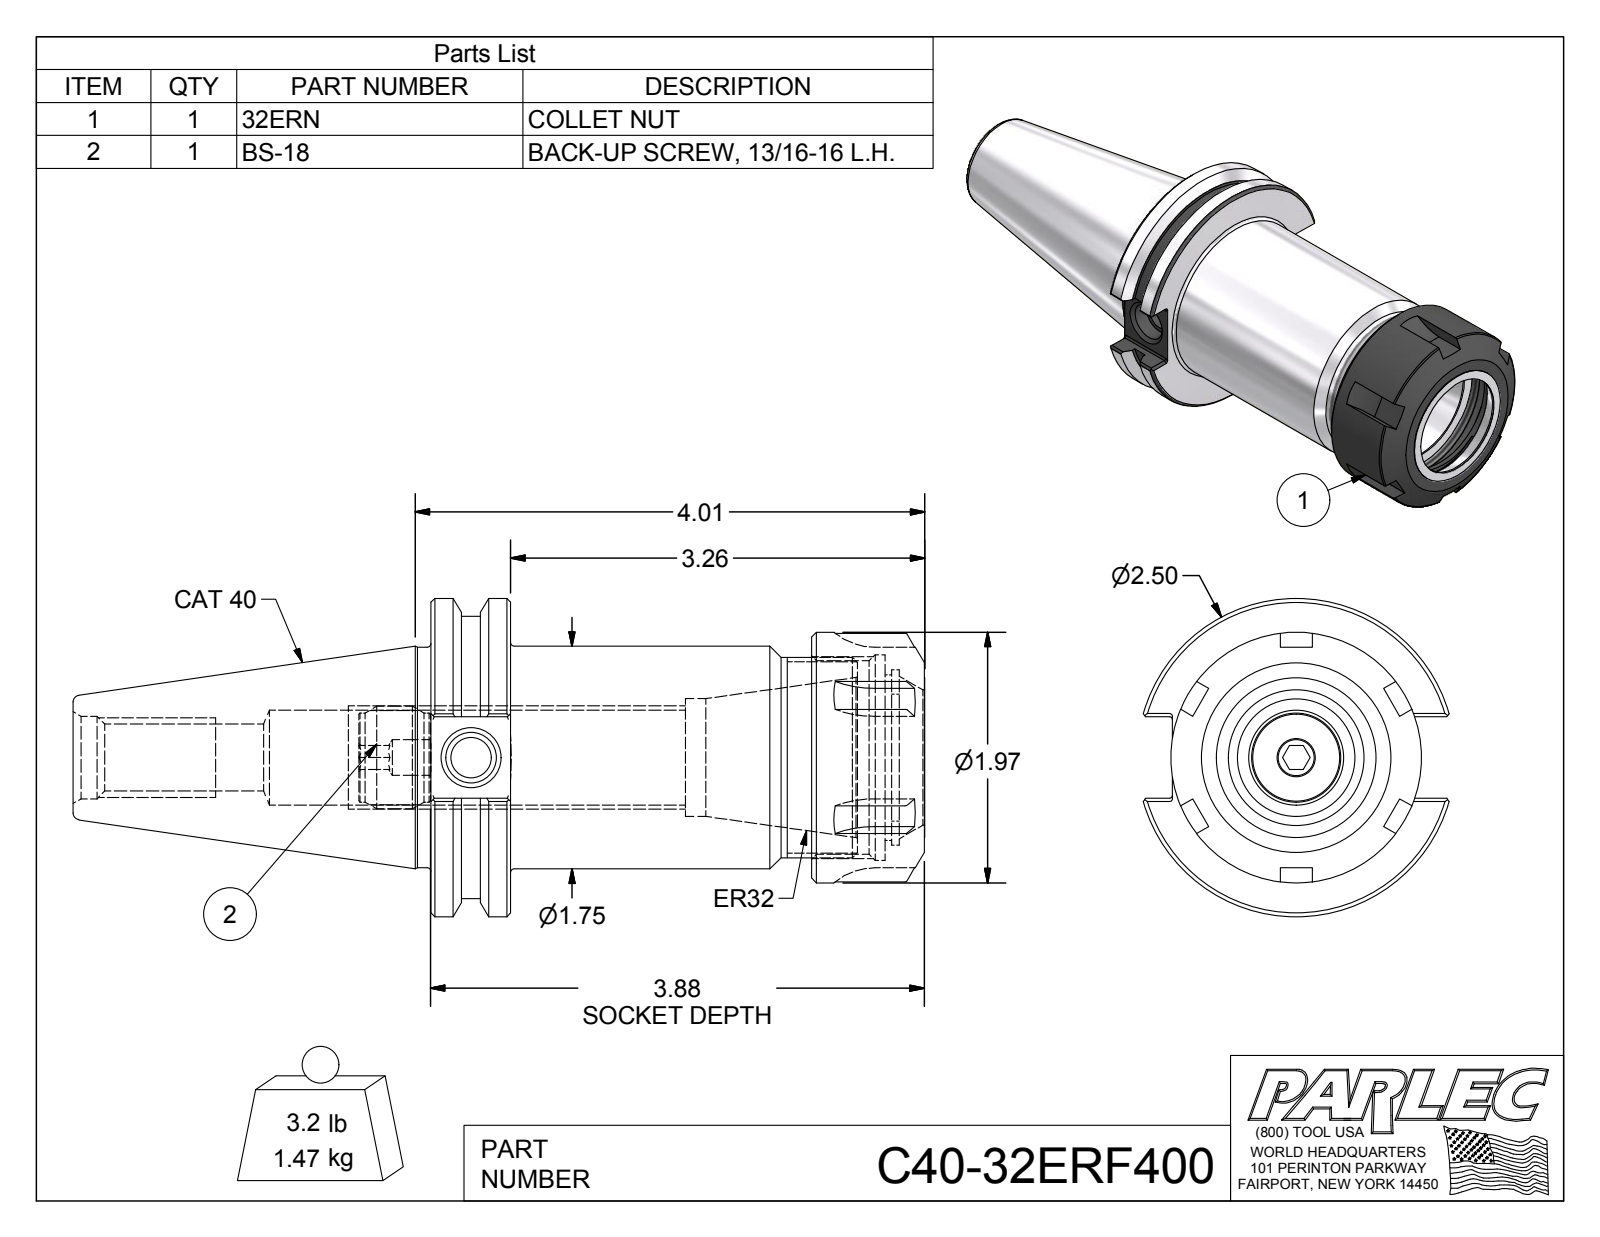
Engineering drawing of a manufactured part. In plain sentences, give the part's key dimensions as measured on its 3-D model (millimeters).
The part is named "C40-32ER4-1; 32ERN; BS-18; C40-32ERF400". Its 3-D file was written by "Autodesk Inventor 2016 (AUTOMOTIVE_DESIGN)". It is 3 solids with 183 faces: 75 planar, 50 cylindrical and 58 other. Overall it measures 169.86 by 63.5 by 61.05 millimeters. Its volume is 187 910 cubic millimeters and its surface area 45 379 square millimeters. Round holes: 1 of diameter 7.11, 1 of diameter 8, 1 of diameter 10.13, 1 of diameter 13.39, 1 of diameter 16.46, 1 of diameter 18.92, 1 of diameter 23.5, 1 of diameter 27, 1 of diameter 33.02, 1 of diameter 38.65, 1 of diameter 41. Round bosses or shafts: 1 of diameter 63.5, 1 of diameter 56.36, 1 of diameter 50, 1 of diameter 44.45, 1 of diameter 43.94, 1 of diameter 40, 1 of diameter 20.45, 1 of diameter 17.78. Partial cylindrical surfaces (rounded edges, fillets, slot ends): 24 of radius 0.51, 1 of radius 14.9, 1 of radius 17.5. The main face-to-face distances are 15.88, 98.43, 82.55, 75.65, 59.77, 22.78, 90.66, 74.78, 15.01, 7.77. The hole center spacings are 1.85.
